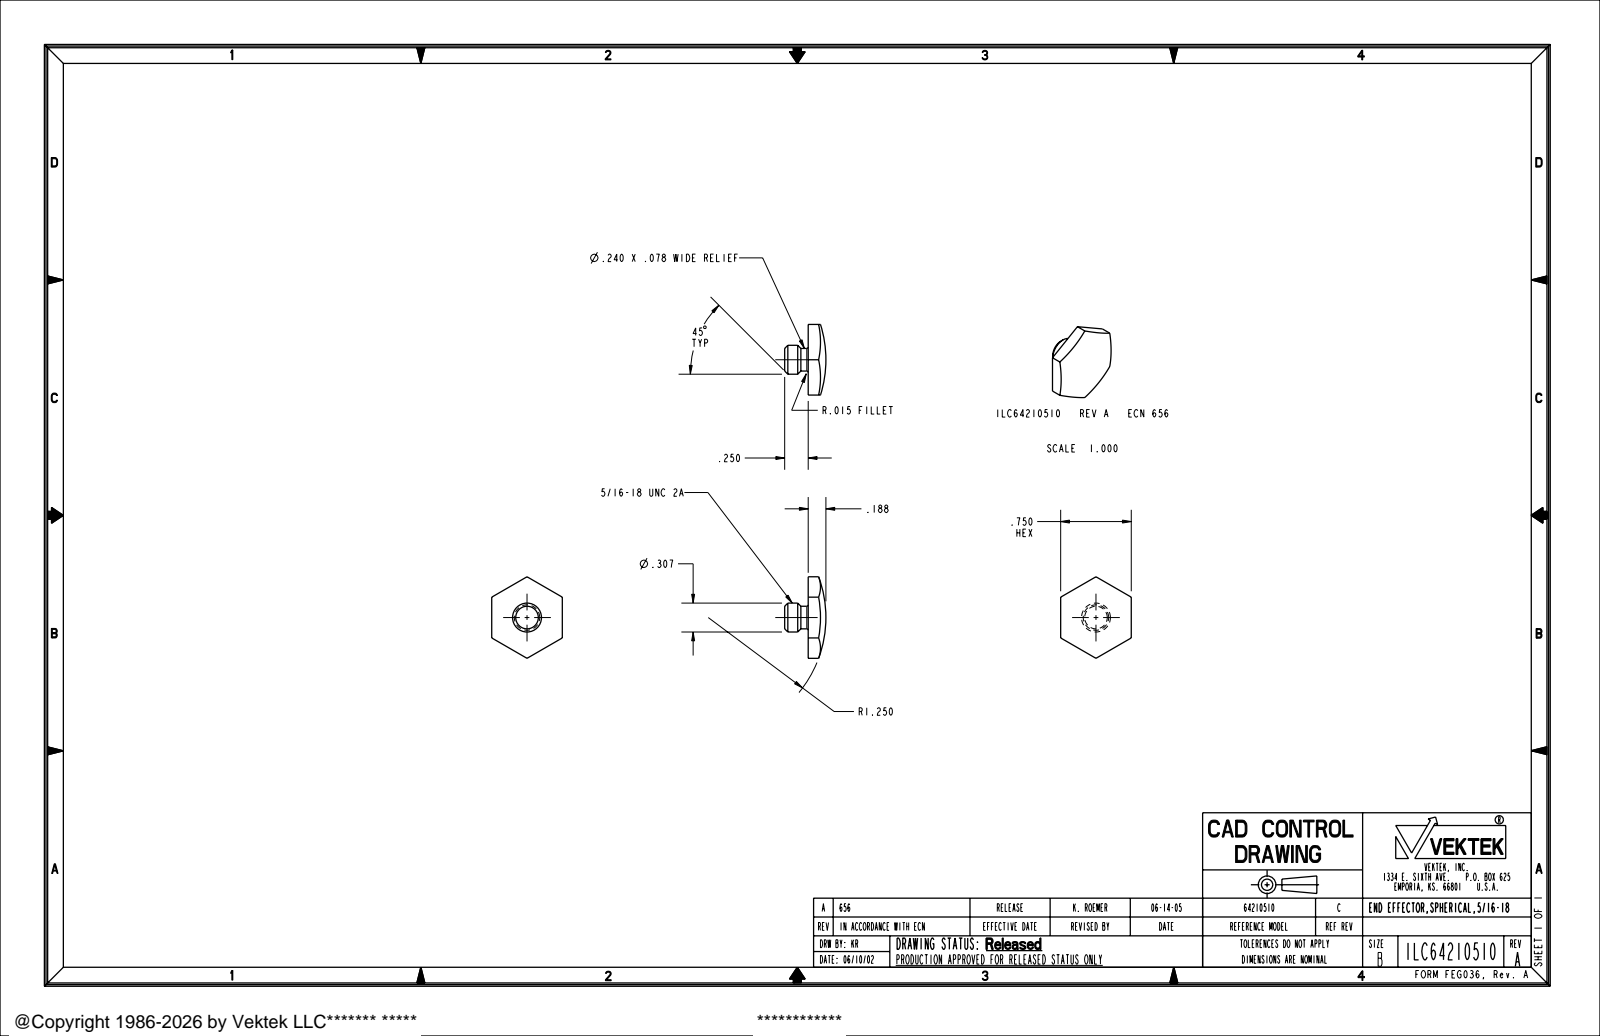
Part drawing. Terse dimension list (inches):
name: ILC64210510
written by: PRO/ENGINEER BY PARAMETRIC TECHNOLOGY CORPORATION, 2004290 (AUTOMOTIVE_DESIGN_CC2)
unit: in
bodies: 1 solid, 20 faces (8 planar, 4 cylindrical, 8 other)
size: 0.866 × 0.75 × 0.438
volume: 0.091 in³; area: 1.546 in²
bosses: 1× ⌀0.307, 1× ⌀0.24
face distances: 0.75, 0.25
